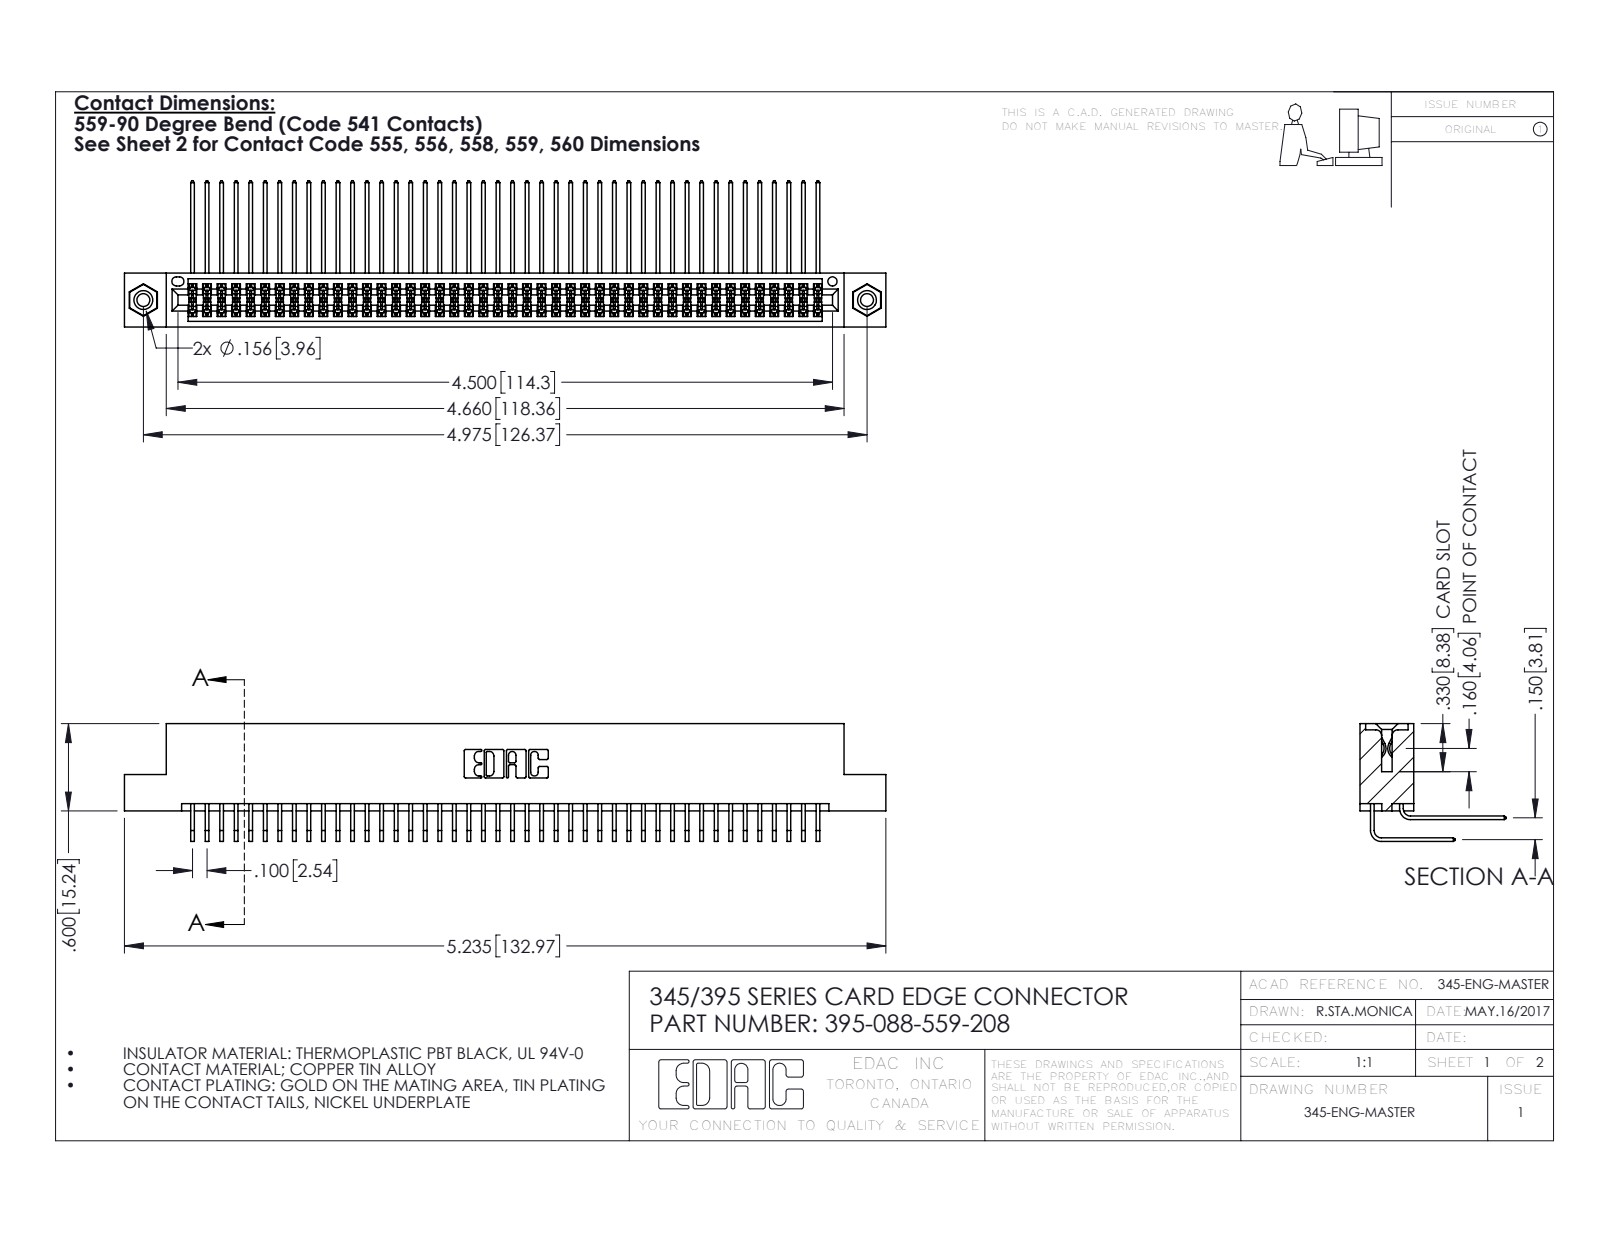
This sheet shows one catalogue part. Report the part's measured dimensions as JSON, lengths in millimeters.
{"part_name": "345-292-001_559 Tail - 2; 395-088-559-208; 345-292-001_558 559 Tail - 1; 345 Part_Flush Mounting Lugs - 0.156 Dia-TI (+1 more)", "step_written_by": "SolidWorks 2016 (CONFIG_CONTROL_DESIGN)", "units": "millimeters", "bodies": {"solids": 91, "faces": 4762, "planar": 3192, "cylindrical": 1554, "other": 16}, "overall_size": [133, 25.5, 20.5], "volume_mm3": 13400, "surface_area_mm2": 22300, "round_holes": [[2.3, 2], [3.2, 2], [4, 2], [1.6, 1]], "round_bosses_or_shafts": [[3.9, 2]], "partial_cylinders_radius": [[0.2, 133], [0.3, 22], [0.2, 6], [0.8, 6], [0.7, 3], [0.4, 2], [0.5, 2], [0.6, 2]], "face_to_face_distances": [1.8, 7.6, 5.1, 9.4, 2.5, 6.9, 0.6, 5.7, 4.4, 3.8], "hole_center_spacings": [6.9, 120.4, 126.4]}
